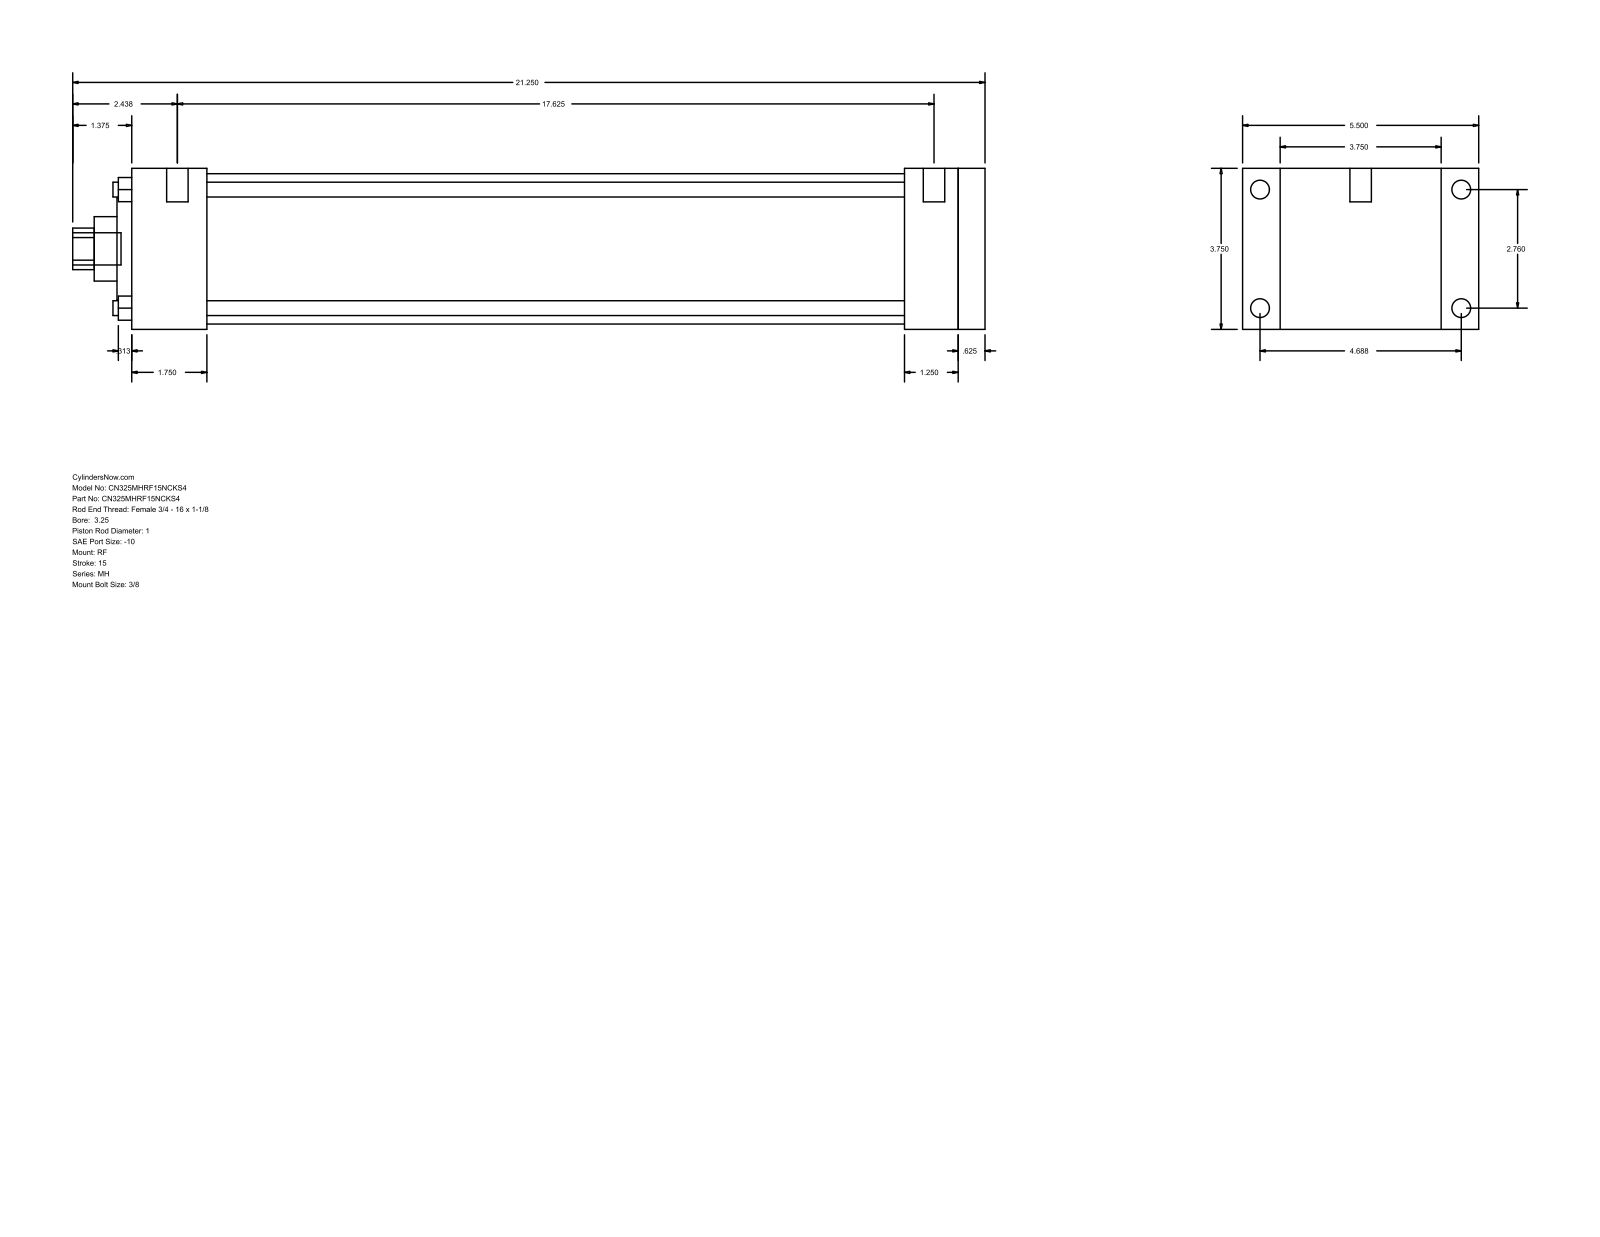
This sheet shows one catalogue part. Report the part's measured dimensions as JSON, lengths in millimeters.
{"part_name": "MH_RF__0325_1", "step_written_by": "GSSL Pune (CONFIG_CONTROL_DESIGN)", "units": "millimeters", "bodies": {"solids": 0, "faces": 94, "planar": 65, "cylindrical": 29, "other": 0}, "overall_size": [539.75, 139.7, 95.25], "round_holes": [[8.76, 4], [25.4, 1], [38.1, 1], [60.33, 1], [88.9, 1]], "round_bosses_or_shafts": [[11.13, 4], [5.56, 4], [12.7, 2], [19.05, 1]], "partial_cylinders_radius": [[12.29, 1]], "face_to_face_distances": [95.24, 504.83, 15.87, 488.96, 22.23, 117.47, 44.46, 444.5, 460.37, 457.2], "hole_center_spacings": [49.57, 70.1, 99.14]}
